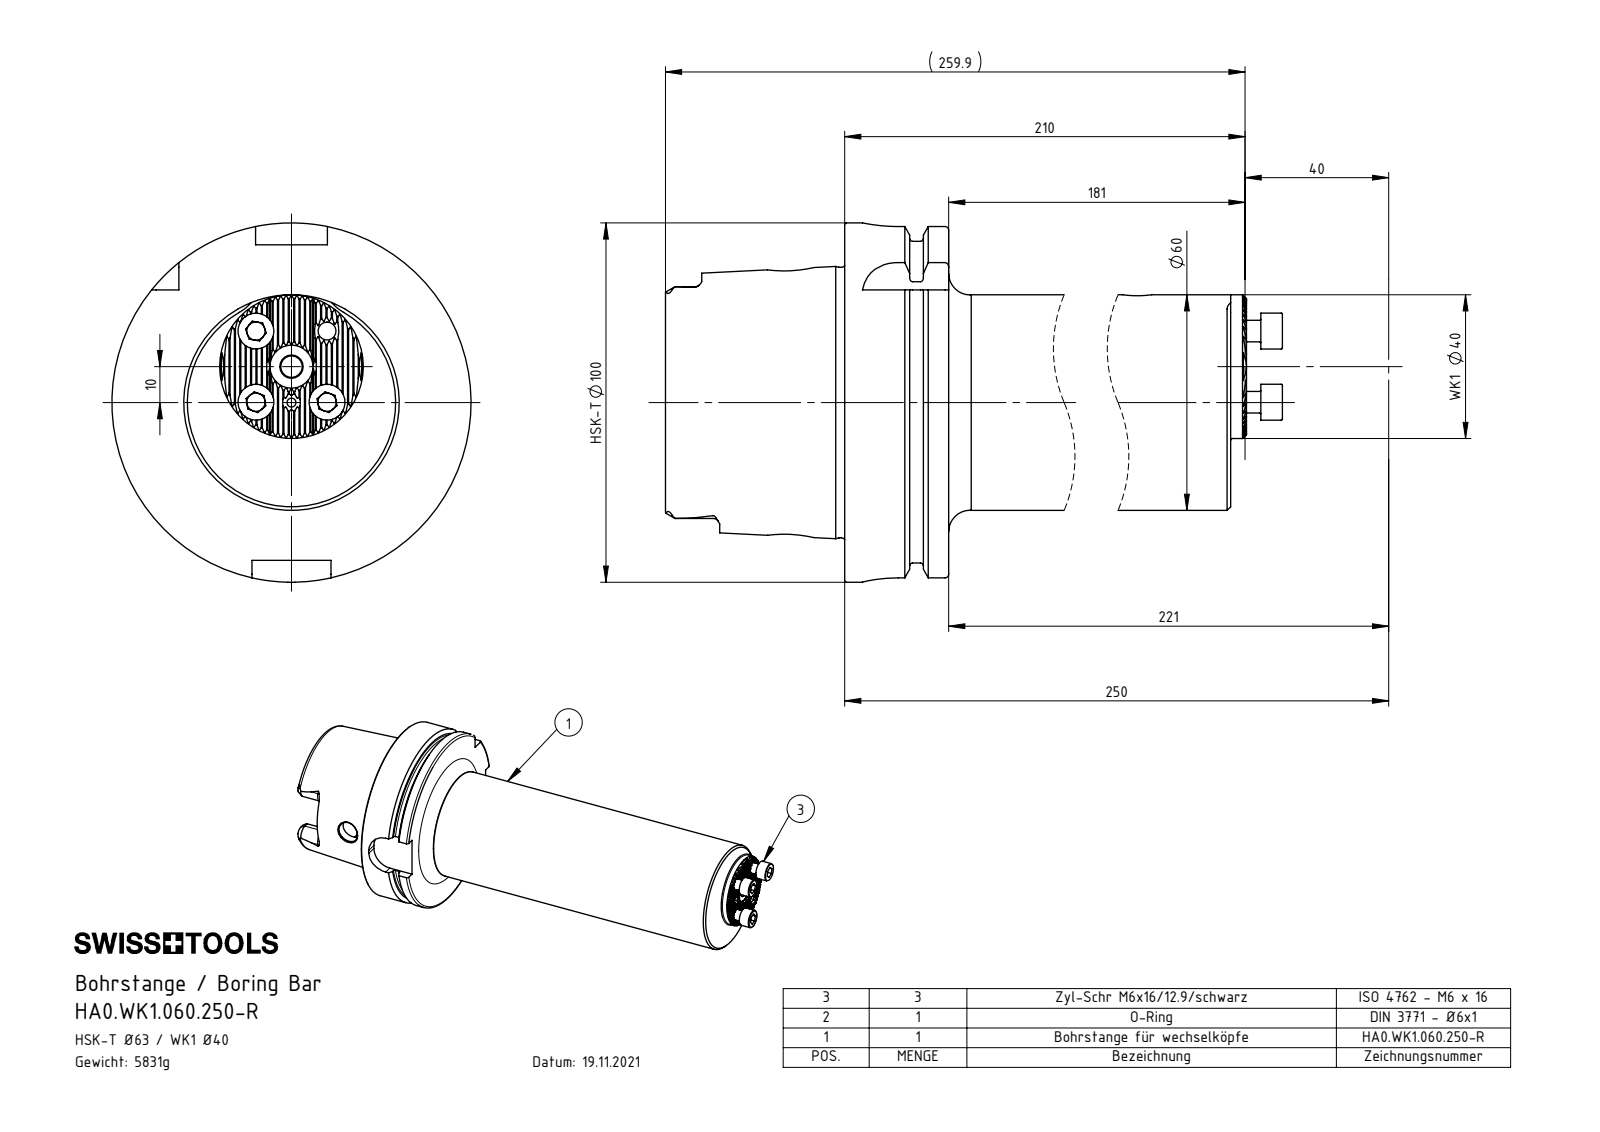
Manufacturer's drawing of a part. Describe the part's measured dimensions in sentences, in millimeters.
The part is named "0-W.1.060.250-R; HA0-WK1.060.250-R_A; ISO 4762 - M6 x 16; KVT_MB_600_080 (+1 more)". Its 3-D file was written by "SolidWorks 2017 (AUTOMOTIVE_DESIGN)". It is 7 solids with 458 faces: 260 planar, 107 cylindrical and 91 other. Overall it measures 270.3 by 100 by 100 millimeters. Its volume is 742 667 cubic millimeters and its surface area 94 001 square millimeters. Round holes: 4 of diameter 5, 2 of diameter 6, 2 of diameter 12, 1 of diameter 2.5, 1 of diameter 7, 1 of diameter 7.4, 1 of diameter 10, 1 of diameter 22.5, 1 of diameter 26, 1 of diameter 53, 1 of diameter 63. Round bosses or shafts: 3 of diameter 10, 3 of diameter 6, 1 of diameter 100, 1 of diameter 91.95, 1 of diameter 75.26, 1 of diameter 60, 1 of diameter 40, 1 of diameter 8. Partial cylindrical surfaces (rounded edges, fillets, slot ends): 27 of radius 0.12, 6 of radius 1.9, 4 of radius 4.88, 4 of radius 10. The main face-to-face distances are 28.95, 12.45, 16.5, 206, 193.55, 177.05, 49.9, 62.35, 78.85, 255.9. The hole center spacings are 14, 19.8, 9.9, 22.23, 28, 10, 195.
